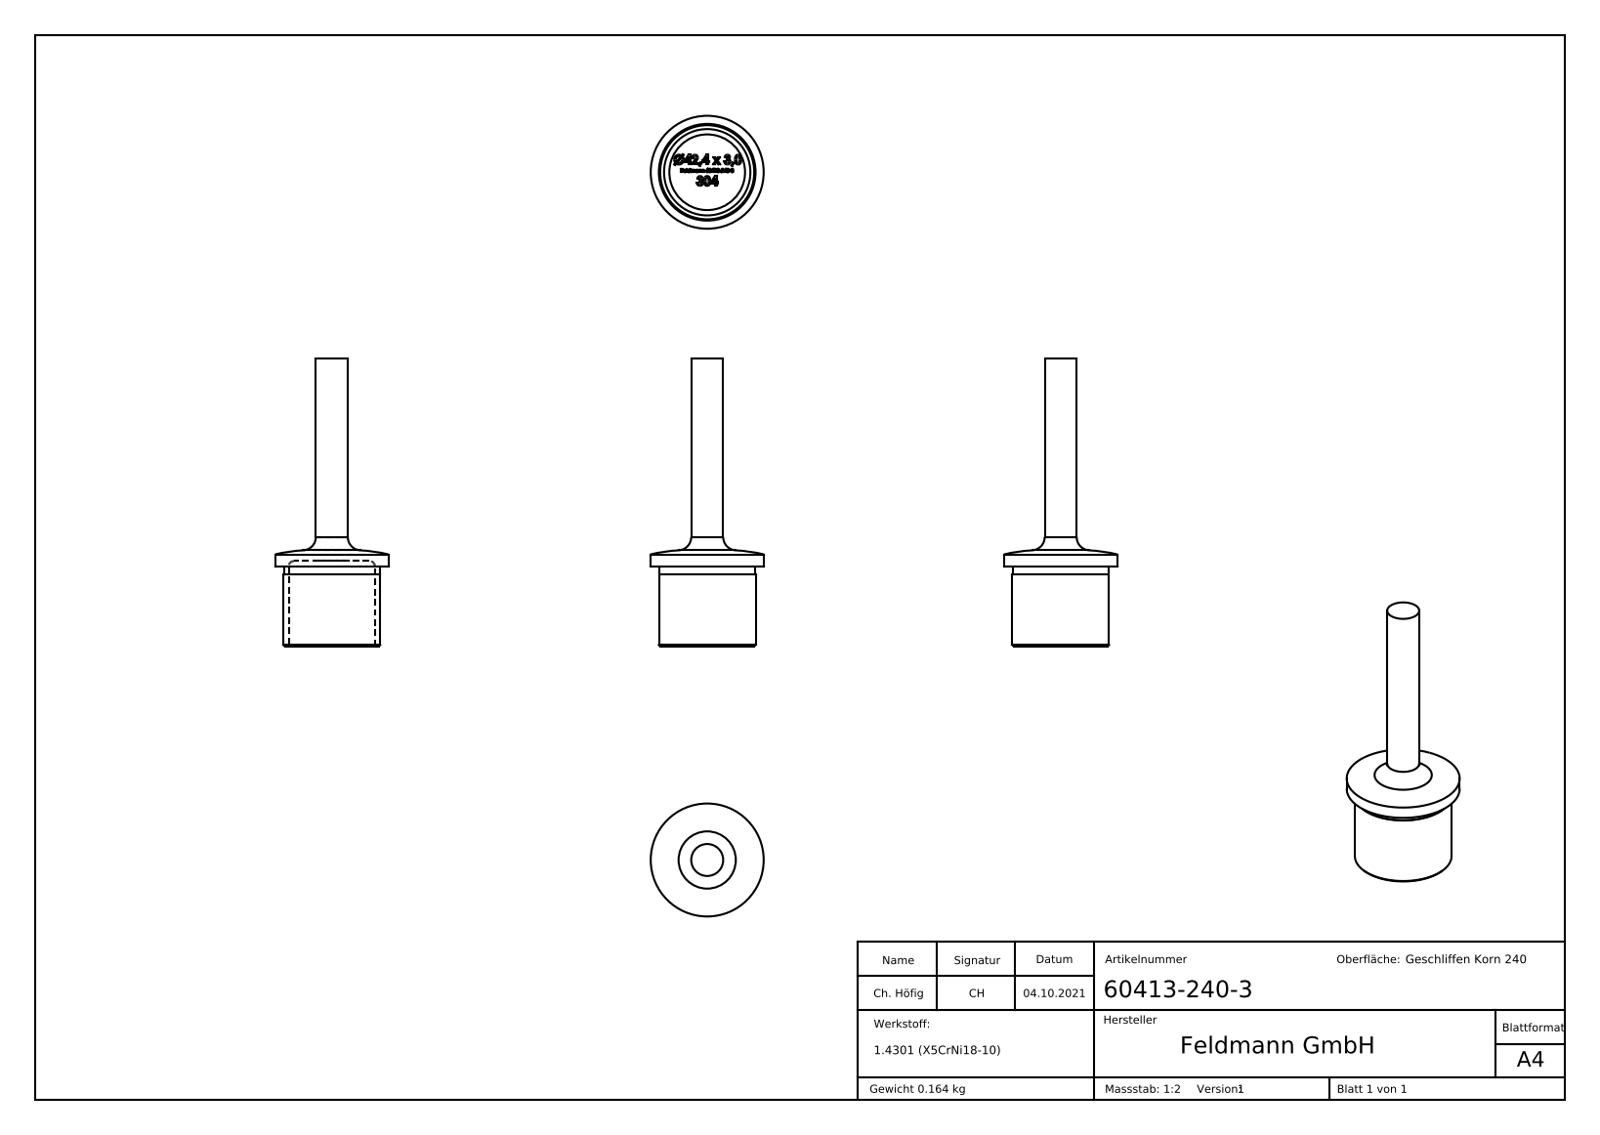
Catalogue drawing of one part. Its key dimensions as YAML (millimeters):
part_name: "60413-240-3"
step_written_by: "SolidWorks 2018 (CONFIG_CONTROL_DESIGN)"
units: millimeters
bodies: {solids: 1, faces: 425, planar: 243, cylindrical: 5, other: 177}
overall_size: [108, 42.4, 42.4]
volume: 20816
surface_area: 12706
round_holes:
  - {diameter: 32.4, count: 1}
round_bosses_or_shafts:
  - {diameter: 42.4, count: 1}
  - {diameter: 36.3, count: 1}
  - {diameter: 35.9, count: 1}
  - {diameter: 12, count: 1}
face_to_face_distances: [2, 30, 32, 108, 78, 76, 32.1, 2.1, 75.9, 3]
